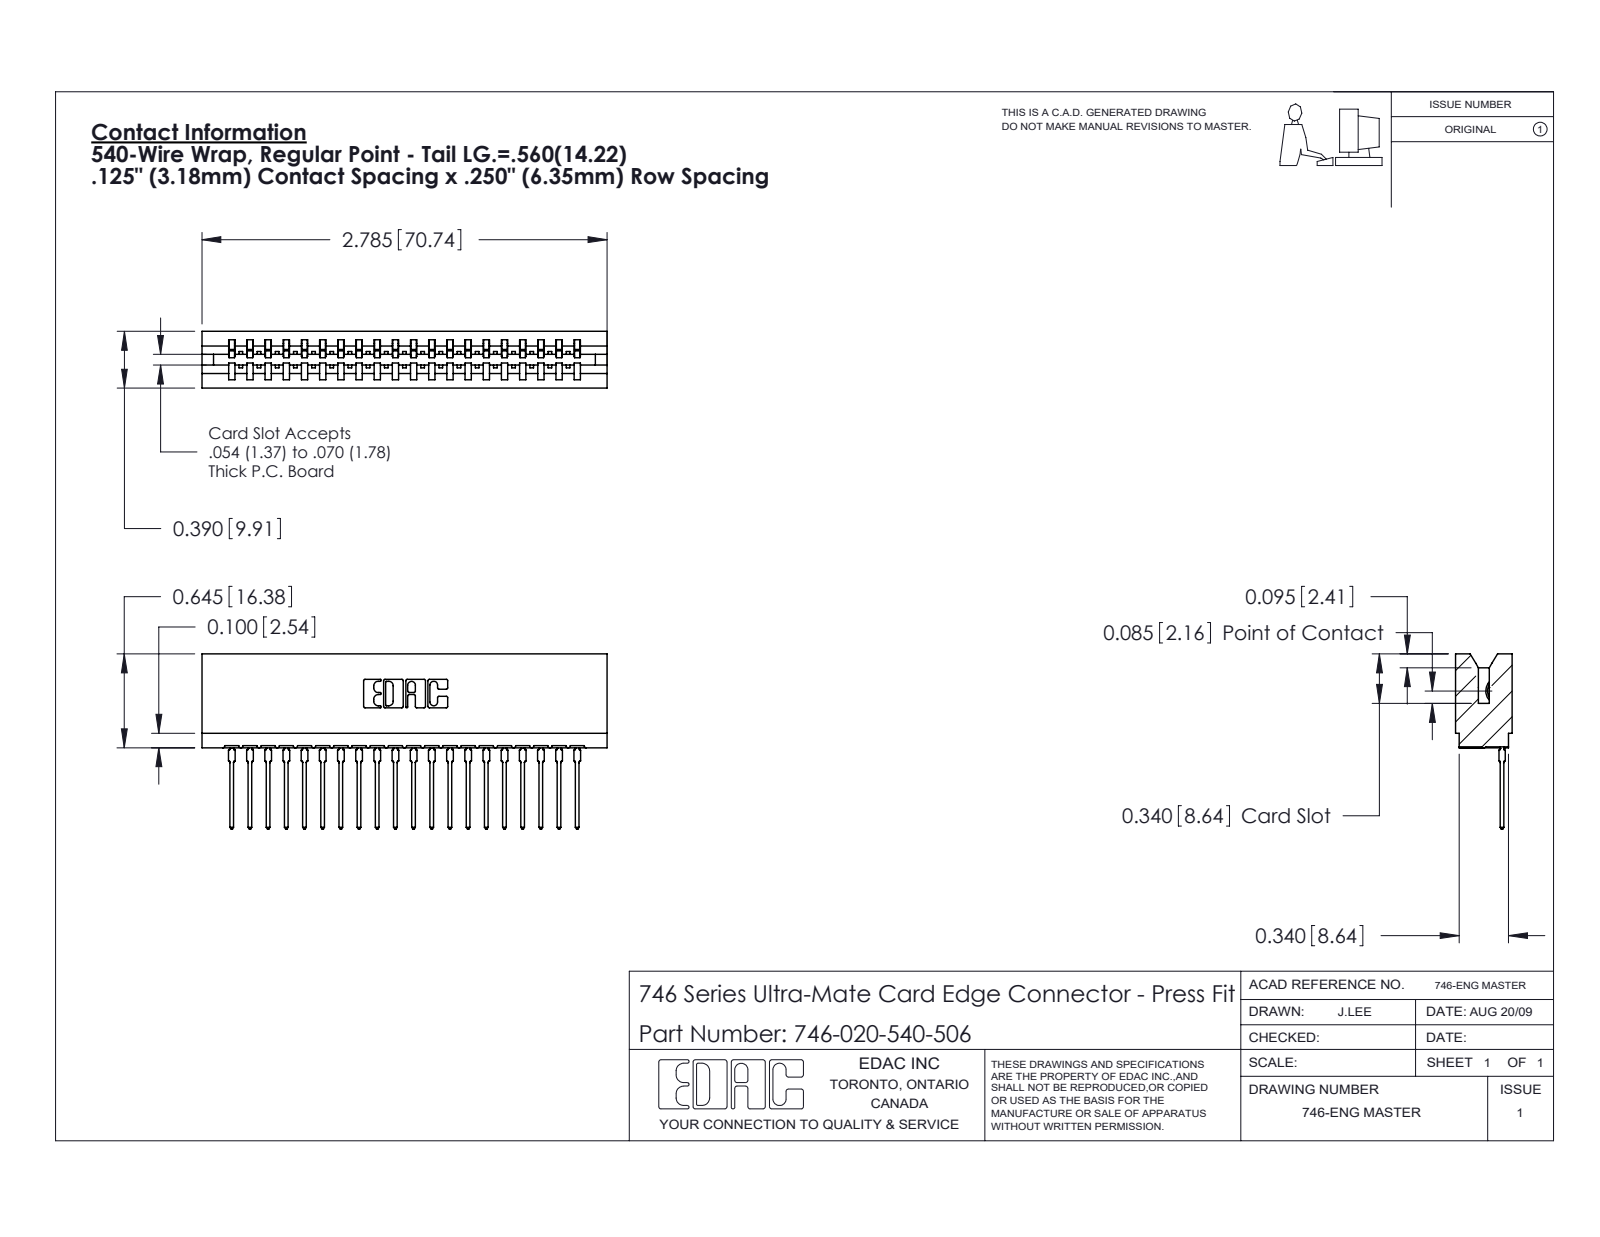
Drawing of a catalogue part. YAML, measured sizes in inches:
part_name: "746-292-001_540; 746-020-540-506; 746 Part_.340 Slot Depth - 06"
step_written_by: "SolidWorks 2020 (CONFIG_CONTROL_DESIGN)"
units: inches
bodies: {solids: 21, faces: 2258, planar: 1316, cylindrical: 422, other: 520}
overall_size: [2.785, 1.204, 0.39]
volume: 0.494
surface_area: 16.81
partial_cylinders:
  - {radius: 0.021, count: 40}
  - {radius: 0.01, count: 22}
  - {radius: 0.015, count: 21}
  - {radius: 0.007, count: 6}
  - {radius: 0.031, count: 6}
  - {radius: 0.005, count: 4}
  - {radius: 0.011, count: 4}
  - {radius: 0.026, count: 3}
face_to_face_distances: [0.25, 0.057, 0.333, 0.39, 0.5, 0.025, 0.307, 0.125, 0.042, 0.125]
